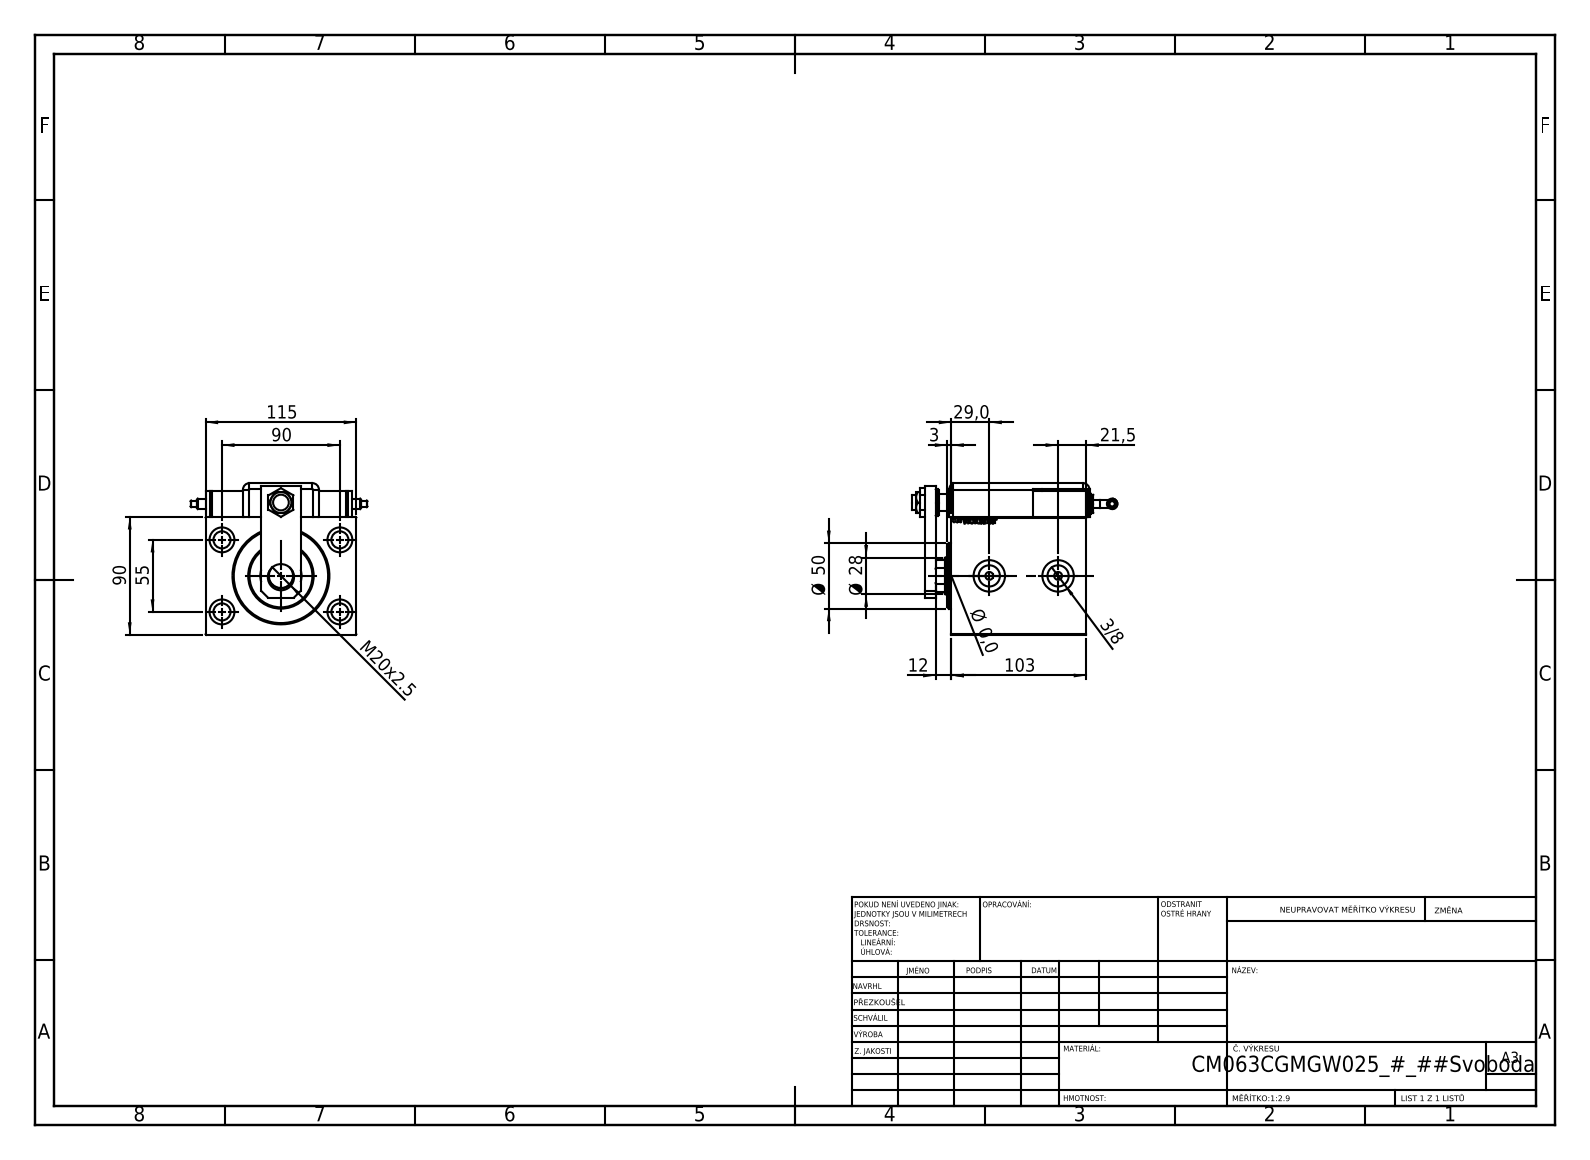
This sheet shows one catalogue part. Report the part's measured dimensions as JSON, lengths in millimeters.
{"part_name": "NUT_D13; MAGNETIC SWITCH Q; ZARAZKA_Q; NUT_D19 (+7 more)", "step_written_by": "SolidWorks 2019 (CONFIG_CONTROL_DESIGN)", "units": "millimeters", "bodies": {"solids": 13, "faces": 1278, "planar": 620, "cylindrical": 125, "other": 533}, "overall_size": [156.46, 135.01, 115.8], "volume_mm3": 1114000, "surface_area_mm2": 179667, "round_holes": [[13, 5], [19, 4], [4, 2], [6, 2], [8, 2], [16.17, 2], [24, 2], [12, 1], [14, 1], [18.5, 1], [20, 1], [28, 1]], "round_bosses_or_shafts": [[20, 3], [16, 2], [14, 2], [8, 2], [6, 2], [5.04, 2], [50, 1]], "partial_cylinders_radius": [[5, 9], [10, 1], [13.5, 1]], "face_to_face_distances": [90, 115, 3, 52, 103, 51, 20, 25.8, 115.8, 8], "hole_center_spacings": [52.74, 53.27, 52.22, 55, 90, 94.85, 105.48, 1]}
